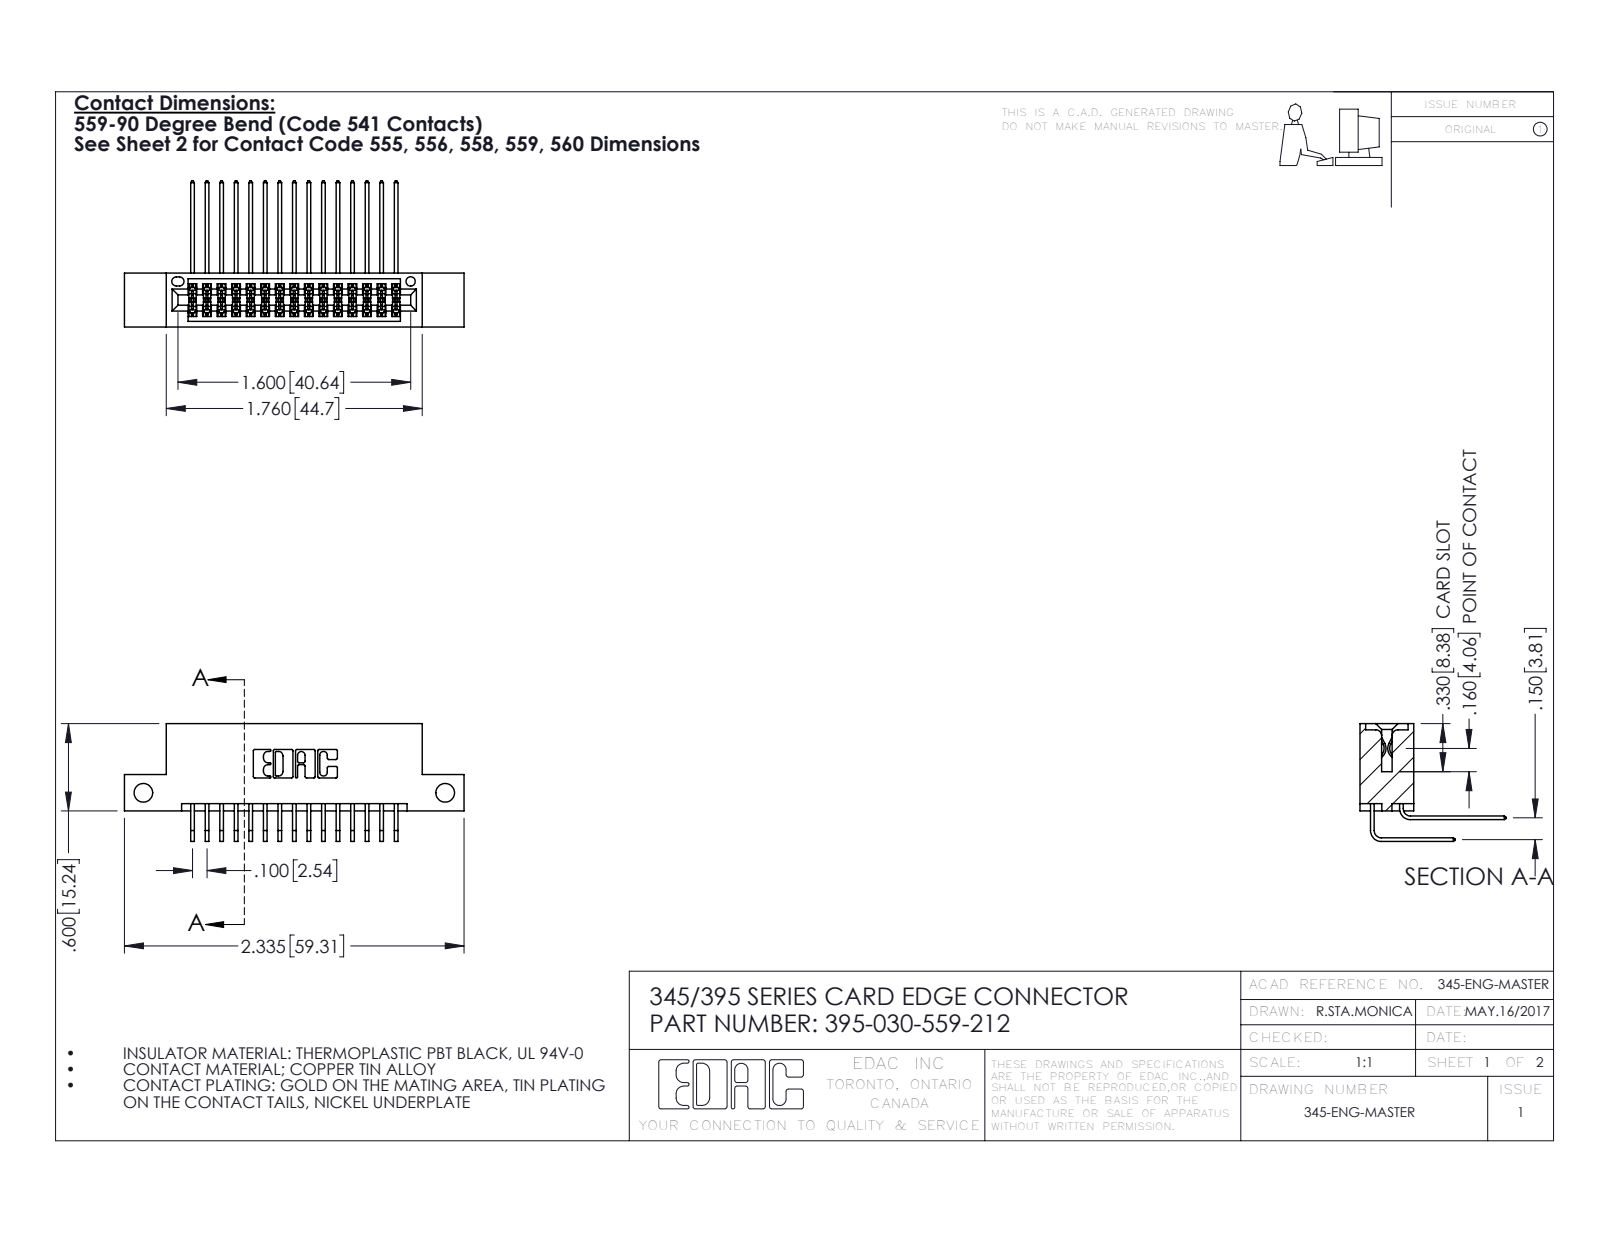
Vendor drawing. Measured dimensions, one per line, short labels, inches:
name: 345-292-001_559 Tail - 2; 395-030-559-212; 345-292-001_558 559 Tail - 1; 345 Part_Flush Mounting Lugs - Side Mount
written by: SolidWorks 2016 (CONFIG_CONTROL_DESIGN)
unit: in
bodies: 31 solids, 1686 faces (1130 planar, 556 cylindrical, 0 other)
size: 2.335 × 1.005 × 0.809
volume: 0.342 in³; area: 13.06 in²
holes: 2× ⌀0.128, 1× ⌀0.064
rounds: 45× R0.006, 22× R0.01, 6× R0.007, 6× R0.031, 3× R0.026, 2× R0.014, 2× R0.019, 2× R0.022
face distances: 0.072, 0.298, 0.2, 0.37, 0.098, 0.272, 0.025, 0.225, 0.15, 0.175
hole spacings: 2.075
